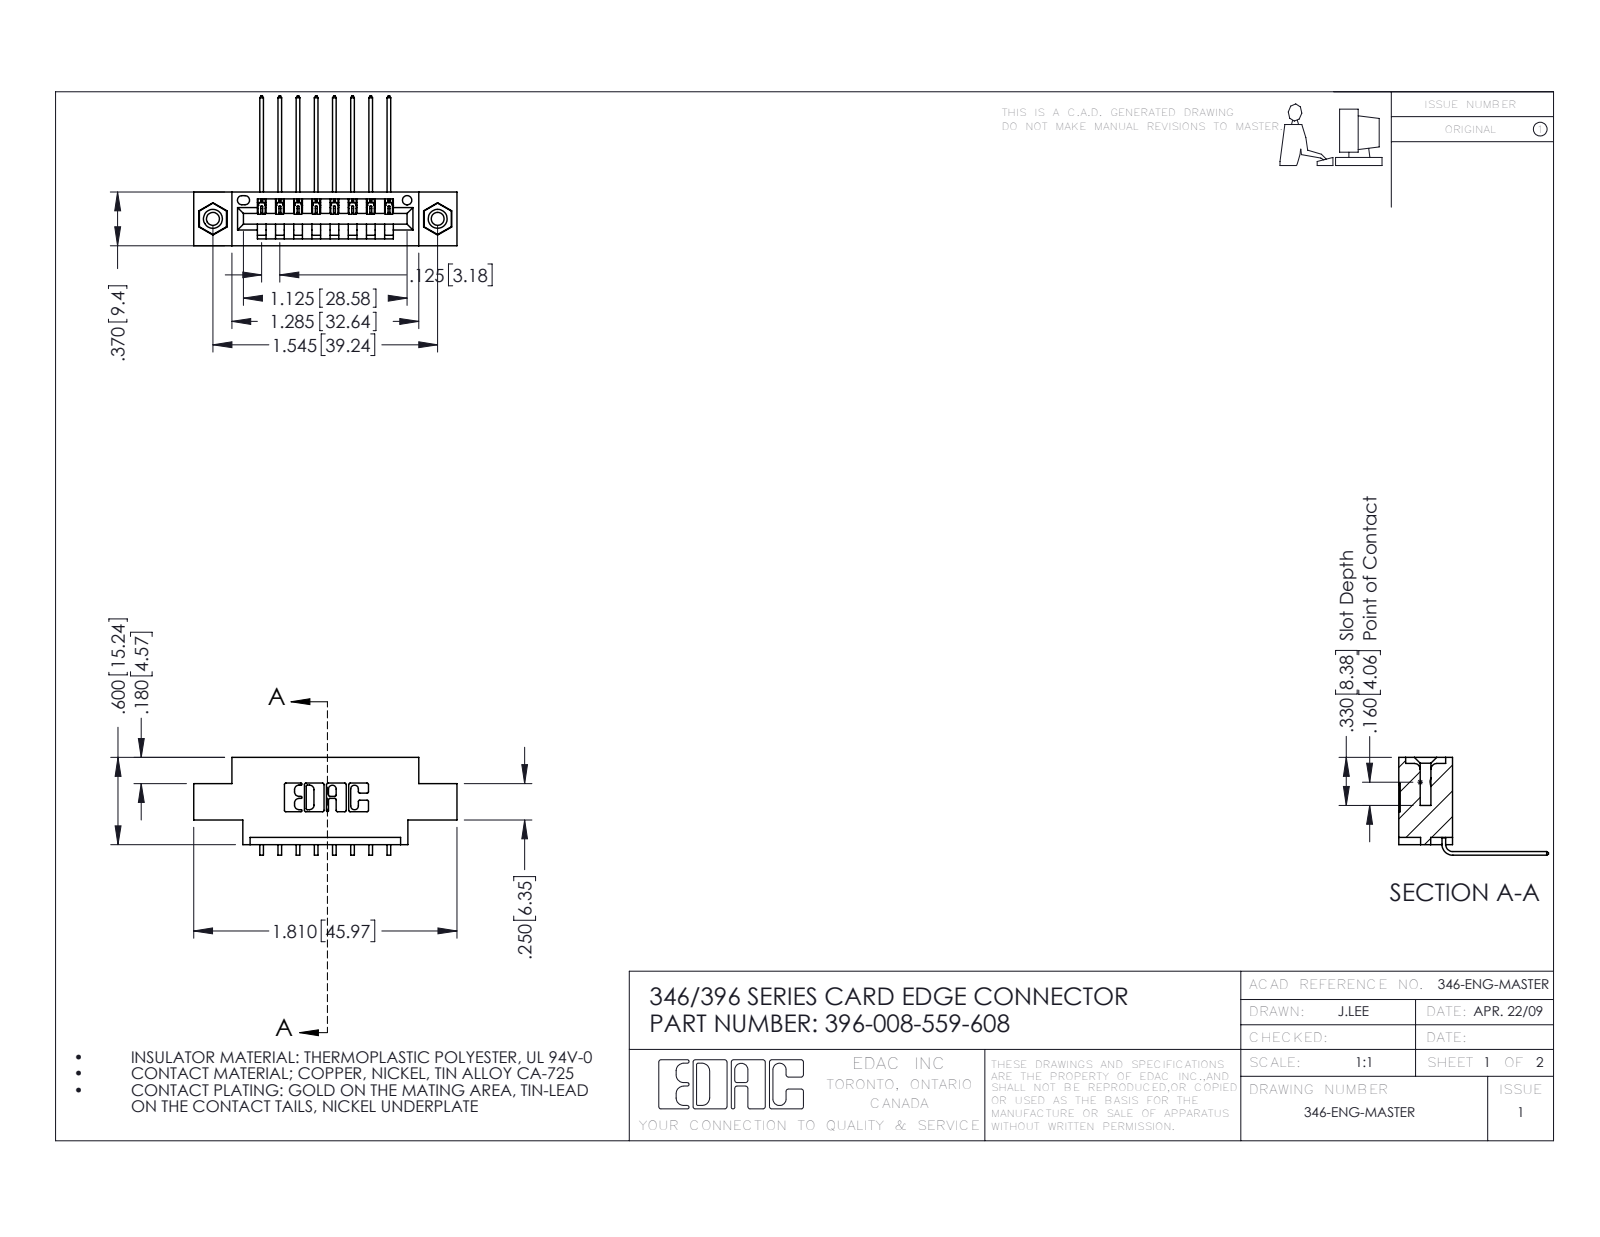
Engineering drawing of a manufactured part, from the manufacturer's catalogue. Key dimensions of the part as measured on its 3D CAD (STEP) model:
Part name (STEP PRODUCT): 346 Part_0.170 Offset - 0.156 Dia-TI; 345-250-001_345-250-003-102; 345-292-001_558 559 Tail - 1; 396-008-559-608
STEP written by: SolidWorks 2016 (CONFIG_CONTROL_DESIGN)
Units: inches
Bodies: 11 solids, 666 faces (448 planar, 202 cylindrical, 16 other)
Overall size (bounding box): 1.81 × 1.03 × 0.673
Volume: 0.246 in³ · Surface area: 7.771 in²
Round holes (diameter × count): ⌀0.089 ×2, ⌀0.125 ×2, ⌀0.156 ×2, ⌀0.064 ×1
Round bosses / shafts (diameter × count): ⌀0.155 ×2
Partial cylindrical surfaces — rounded edges, fillets, slot ends (radius × count): R0.01 ×22, R0.006 ×16, R0.007 ×6, R0.031 ×6, R0.026 ×3, R0.031 ×2, R0.04 ×2, R0.014 ×1
Main face-to-face distances: 0.25, 0.37, 0.048, 0.322, 0.025, 0.072, 0.222, 0.148, 0.1, 0.174
Hole centre spacings: 0.246, 1.341, 1.545
